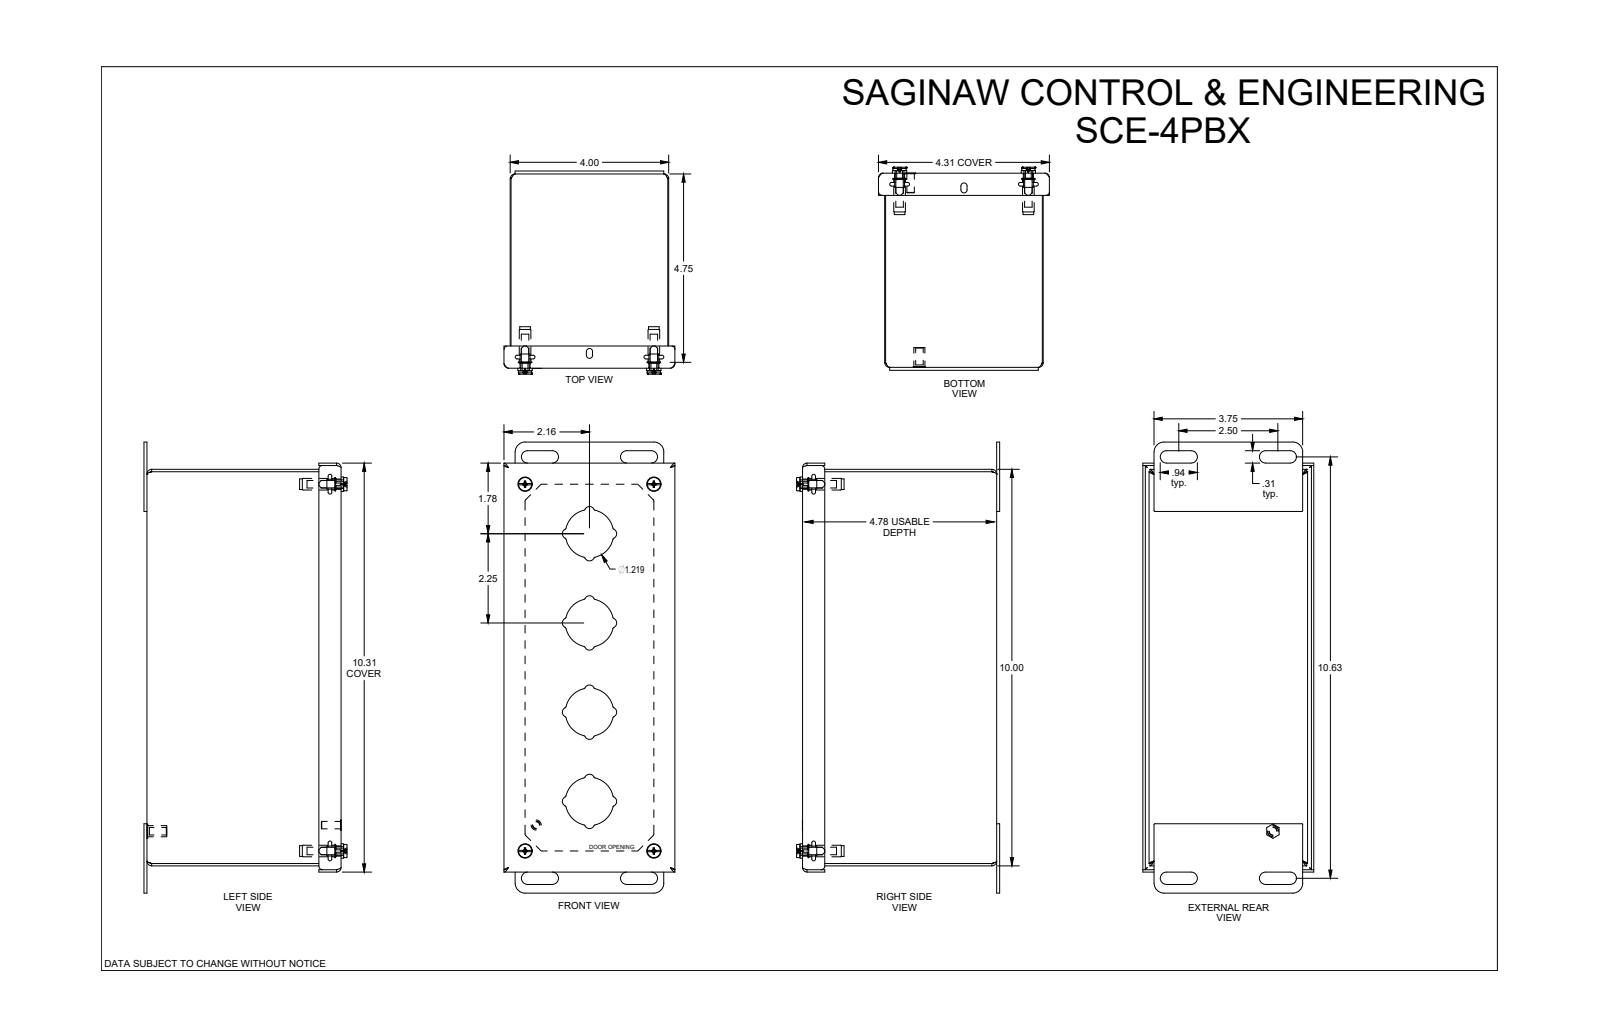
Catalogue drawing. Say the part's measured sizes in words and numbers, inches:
The part is named "SCE-4PBX". Its 3-D file was written by "SolidWorks 2021 (AUTOMOTIVE_DESIGN)". It is 3 solids with 480 faces: 153 planar, 243 cylindrical and 84 other. Overall it measures 11.375 by 5.036 by 4.313 inches. Its volume is 15.55 cubic inches and its surface area 502.3 square inches. Round holes: 5 of diameter 0.19, 4 of diameter 0.22, 4 of diameter 0.25, 4 of diameter 0.266, 4 of diameter 0.317. Round bosses or shafts: 4 of diameter 0.362, 4 of diameter 0.34, 4 of diameter 0.292, 4 of diameter 0.27, 4 of diameter 0.26, 1 of diameter 0.28, 1 of diameter 0.256, 1 of diameter 0.188. Partial cylindrical surfaces (rounded edges, fillets, slot ends): 32 of radius 0.04, 20 of radius 0.06, 16 of radius 0.125, 8 of radius 0.015, 8 of radius 0.115, 8 of radius 0.156, 8 of radius 0.245, 4 of radius 0.02. The main face-to-face distances are 0.06, 3.94, 4.838, 4, 3.88, 4.778, 9.94, 4.898, 0.156, 4.096. The hole center spacings are 3.25, 9.25, 9.25, 9.804, 9.804, 3.25, 3.25, 9.172.
